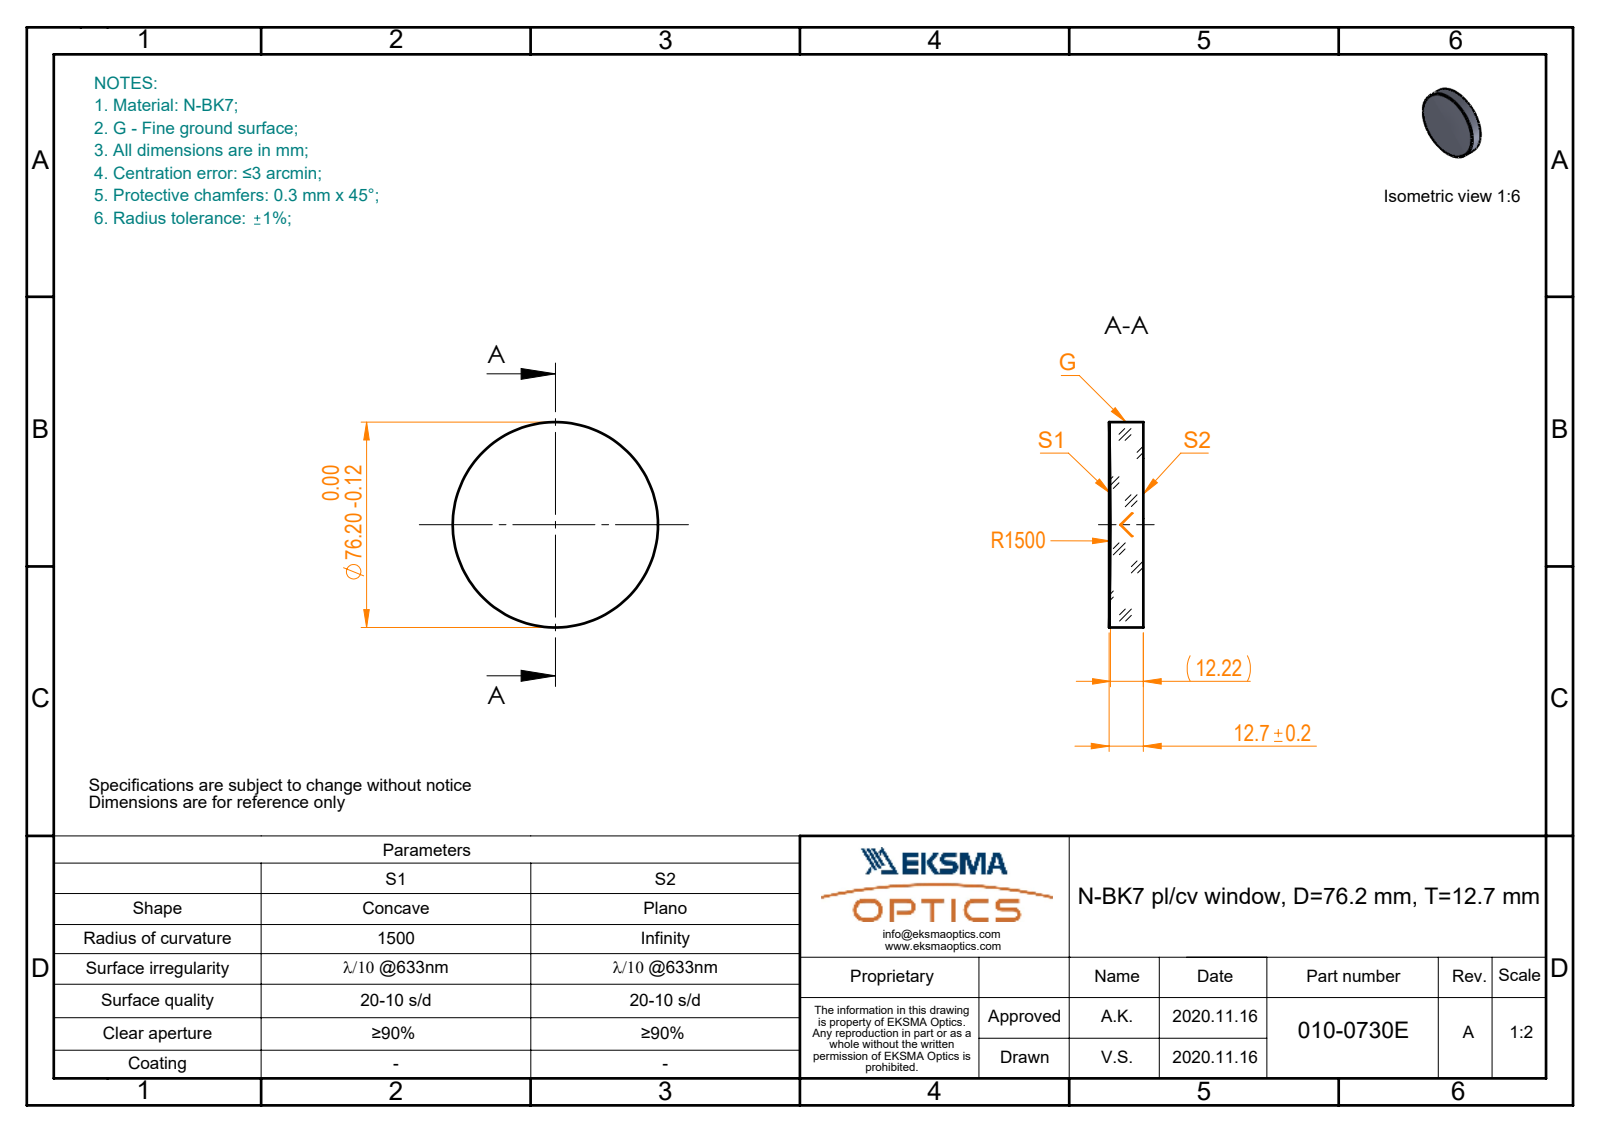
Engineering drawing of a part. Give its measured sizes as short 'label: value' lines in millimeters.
name: 010-0730E_N-BK7_PCV_window
written by: SolidWorks 2019 (CONFIG_CONTROL_DESIGN)
unit: mm
bodies: 1 solid, 5 faces (1 planar, 2 cylindrical, 2 other)
size: 76.2 × 76.2 × 12.7
volume: 56 813 mm³; area: 12 162 mm²
bosses: 1× ⌀76.2
